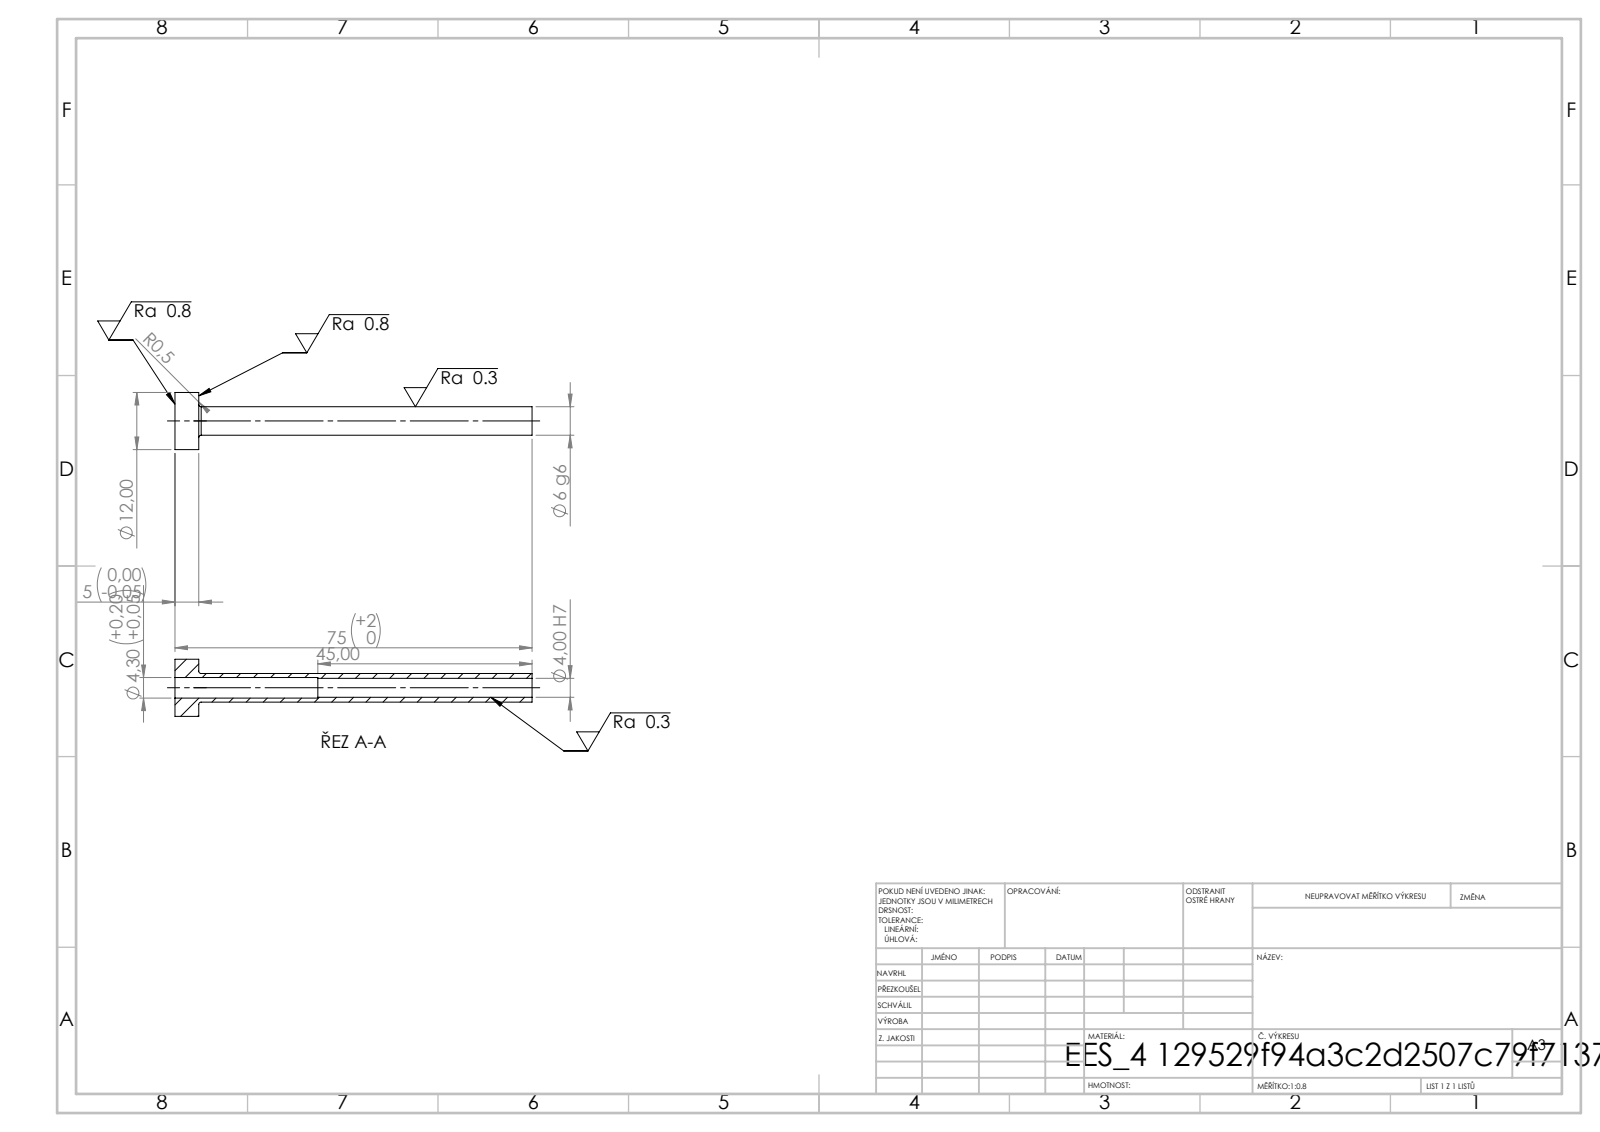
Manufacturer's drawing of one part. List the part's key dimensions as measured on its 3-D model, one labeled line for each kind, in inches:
STEP written by: SolidWorks 2019 (CONFIG_CONTROL_DESIGN)
Units: inches
Bodies: 1 solid, 14 faces (4 planar, 8 cylindrical, 2 other)
Overall size (bounding box): 2.953 × 0.472 × 0.472
Volume: 0.094 in³ · Surface area: 4.148 in²
Round holes (diameter × count): ⌀0.157 ×1, ⌀0.169 ×1
Round bosses / shafts (diameter × count): ⌀0.472 ×1, ⌀0.236 ×1
Main face-to-face distances: 0.197, 2.953, 2.756, 1.181, 0.984, 1.772
